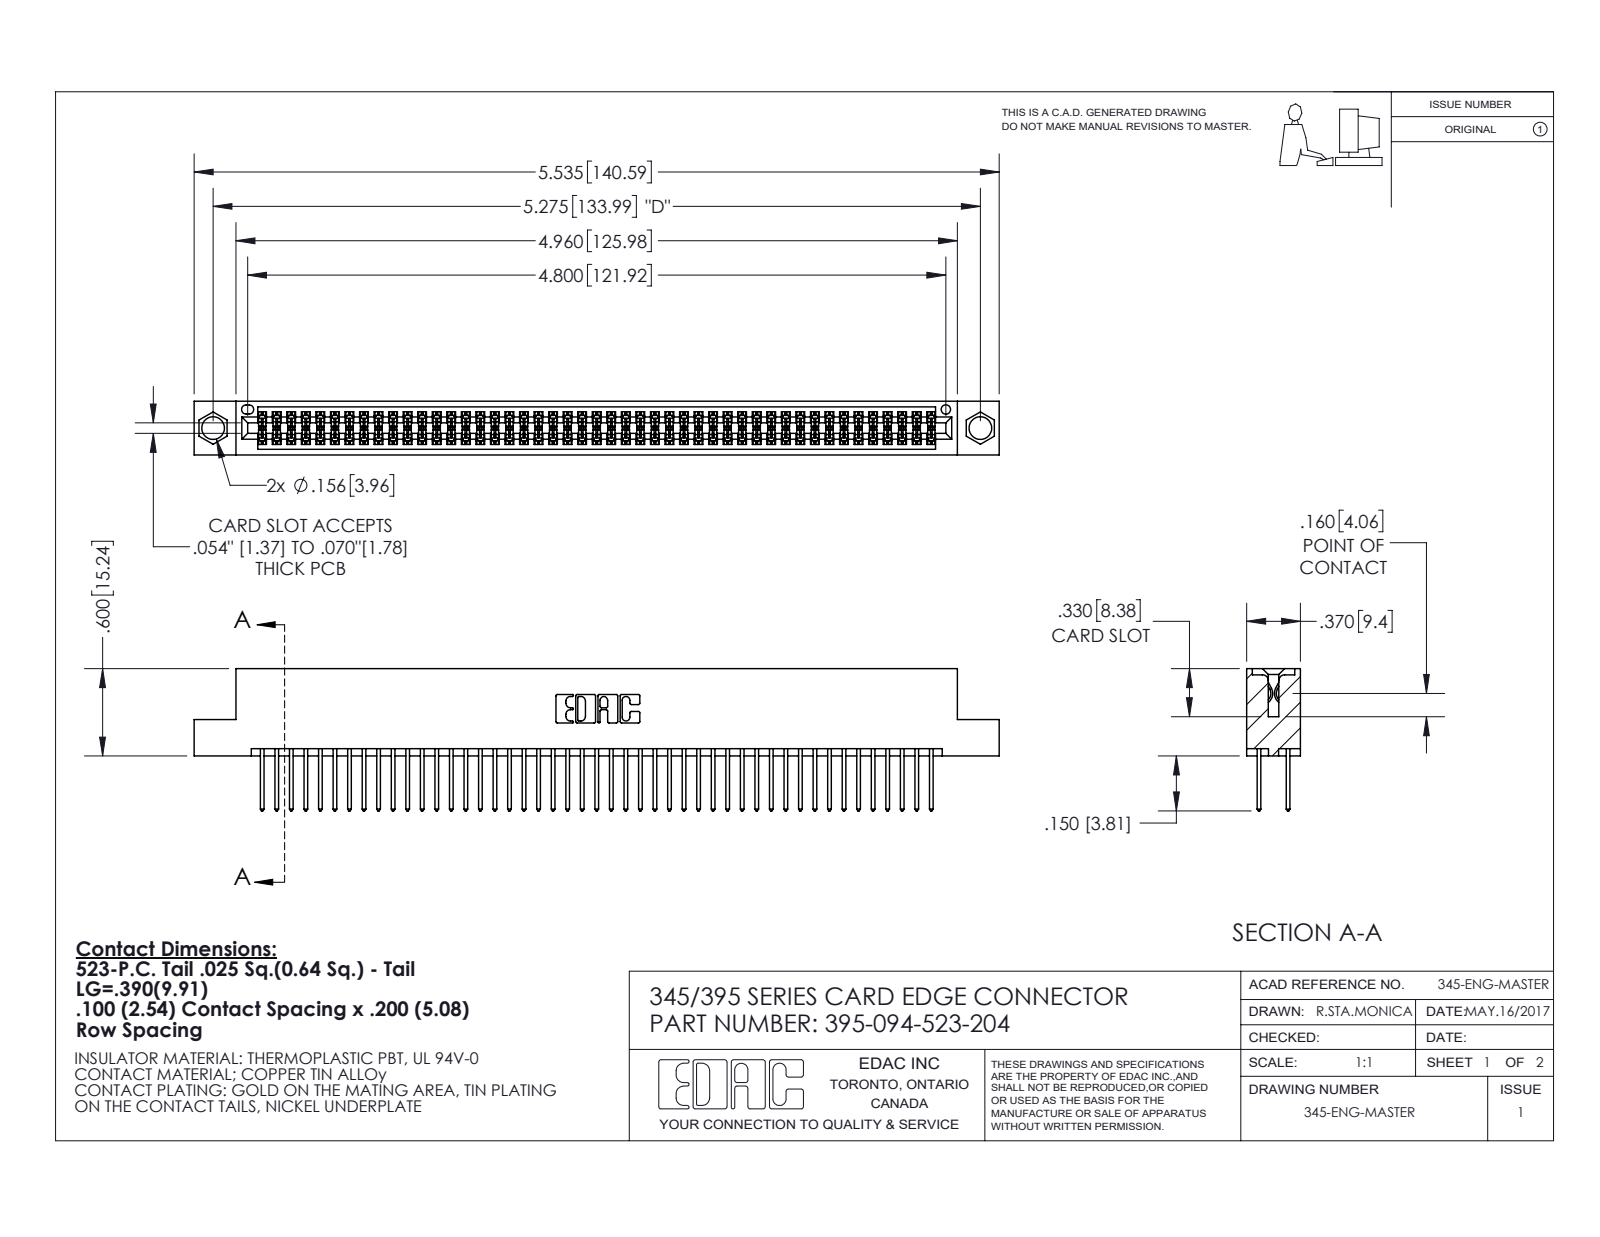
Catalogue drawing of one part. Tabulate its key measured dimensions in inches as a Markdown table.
| quantity | value |
| --- | --- |
| part name | 345 Part_Flush Mounting Lugs - 0.156 Dia-TI; 345-292-001_345-293-123; 395-094-523-204 |
| STEP written by | SolidWorks 2020 (CONFIG_CONTROL_DESIGN) |
| units | inches |
| bodies | 95 solids, 4840 faces (3196 planar, 1644 cylindrical, 0 other) |
| overall size | 5.535 × 0.977 × 0.37 |
| volume | 0.842 in³ |
| surface area | 32.86 in² |
| round holes (diameter × count) | 0.156 × 2, 0.064 × 1 |
| partial cylindrical surfaces (radius × count) | 0.006 × 188, 0.01 × 94, 0.01 × 22, 0.007 × 6, 0.031 × 6, 0.026 × 3, 0.014 × 2, 0.019 × 2 |
| main face-to-face distances | 0.072, 0.298, 0.2, 0.098, 0.272, 0.025, 0.37, 0.225, 0.175, 0.149 |
| hole center spacings | 0.27, 5.039, 5.275 |
